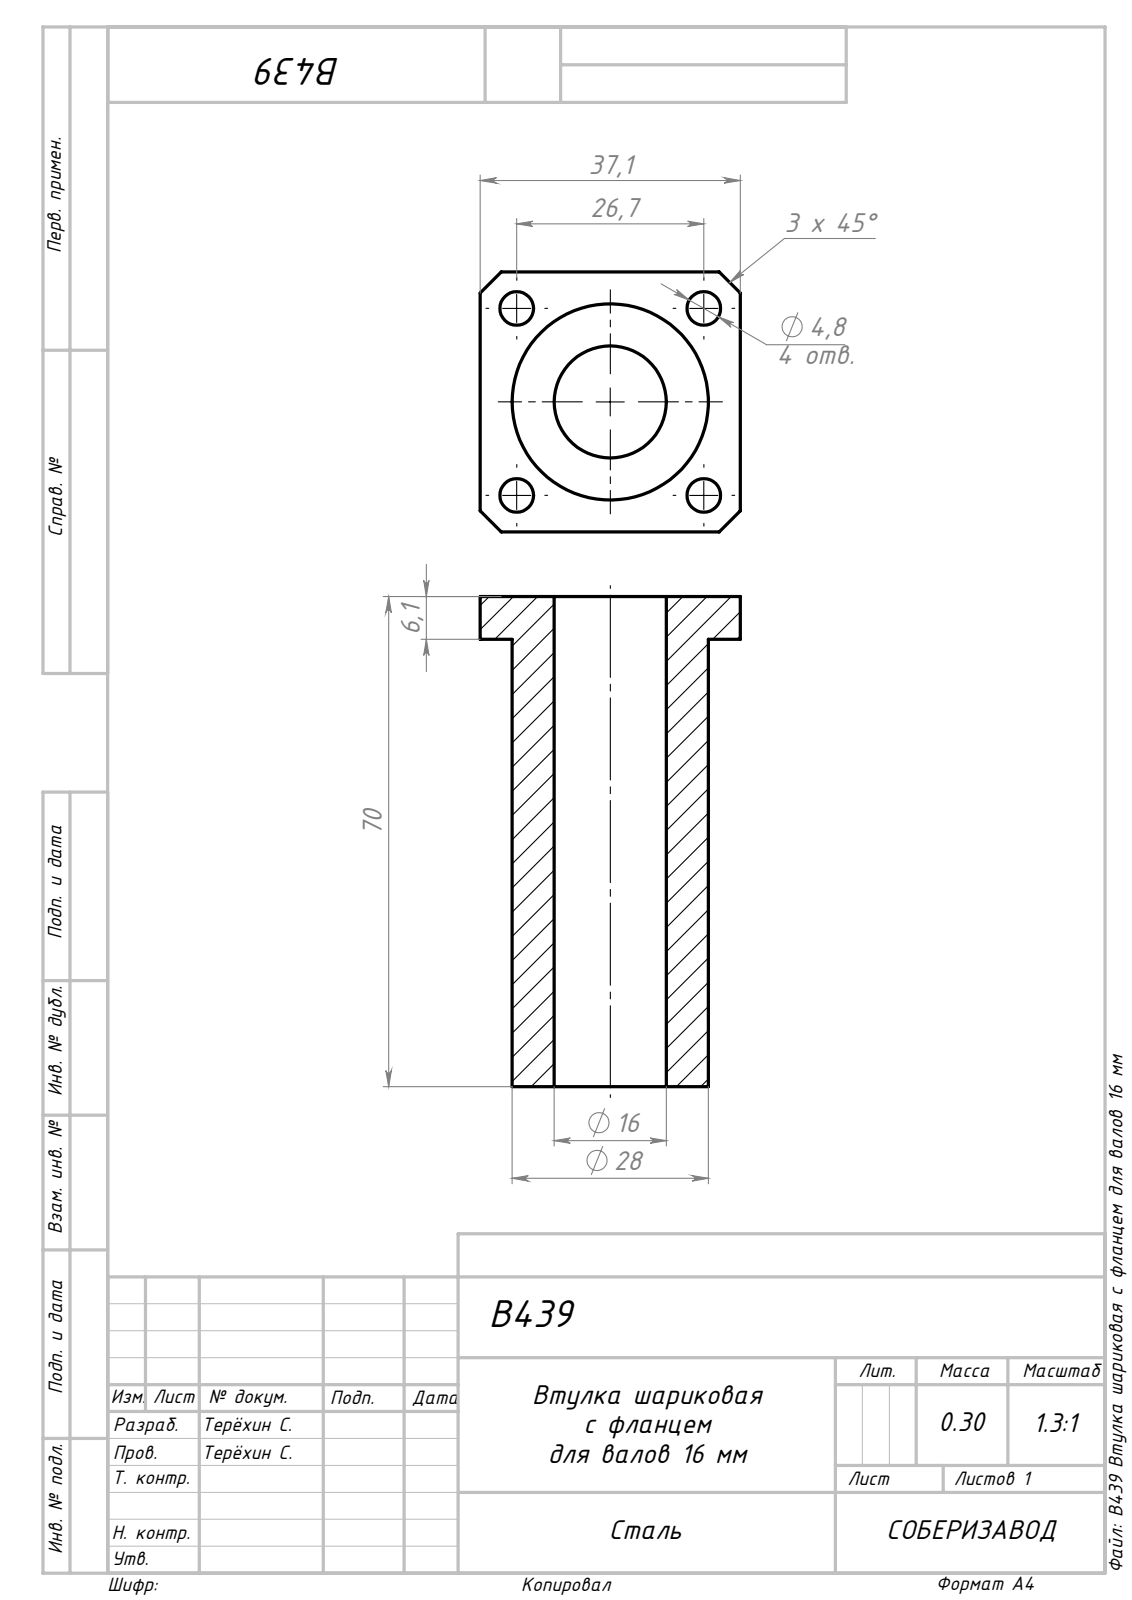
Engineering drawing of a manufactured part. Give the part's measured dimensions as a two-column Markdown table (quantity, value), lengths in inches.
| quantity | value |
| --- | --- |
| part name | Сборка2; B439 Втулка шариковая с фланцем для валов 16 мм_00 |
| STEP written by | SolidWorks 2022 (AUTOMOTIVE_DESIGN) |
| units | inches |
| bodies | 1 solid, 47 faces (15 planar, 24 cylindrical, 8 other) |
| overall size | 2.756 × 1.461 × 1.461 |
| volume | 1.982 in³ |
| surface area | 19.63 in² |
| round holes (diameter × count) | 0.189 × 4, 0.315 × 4, 0.63 × 1 |
| round bosses / shafts (diameter × count) | 1.102 × 1 |
| main face-to-face distances | 0.24, 2.756, 2.516, 1.461, 0.177, 0.063, 2.579, 1.898, 1.898 |
| hole center spacings | 0.743, 1.051, 1.487 |
